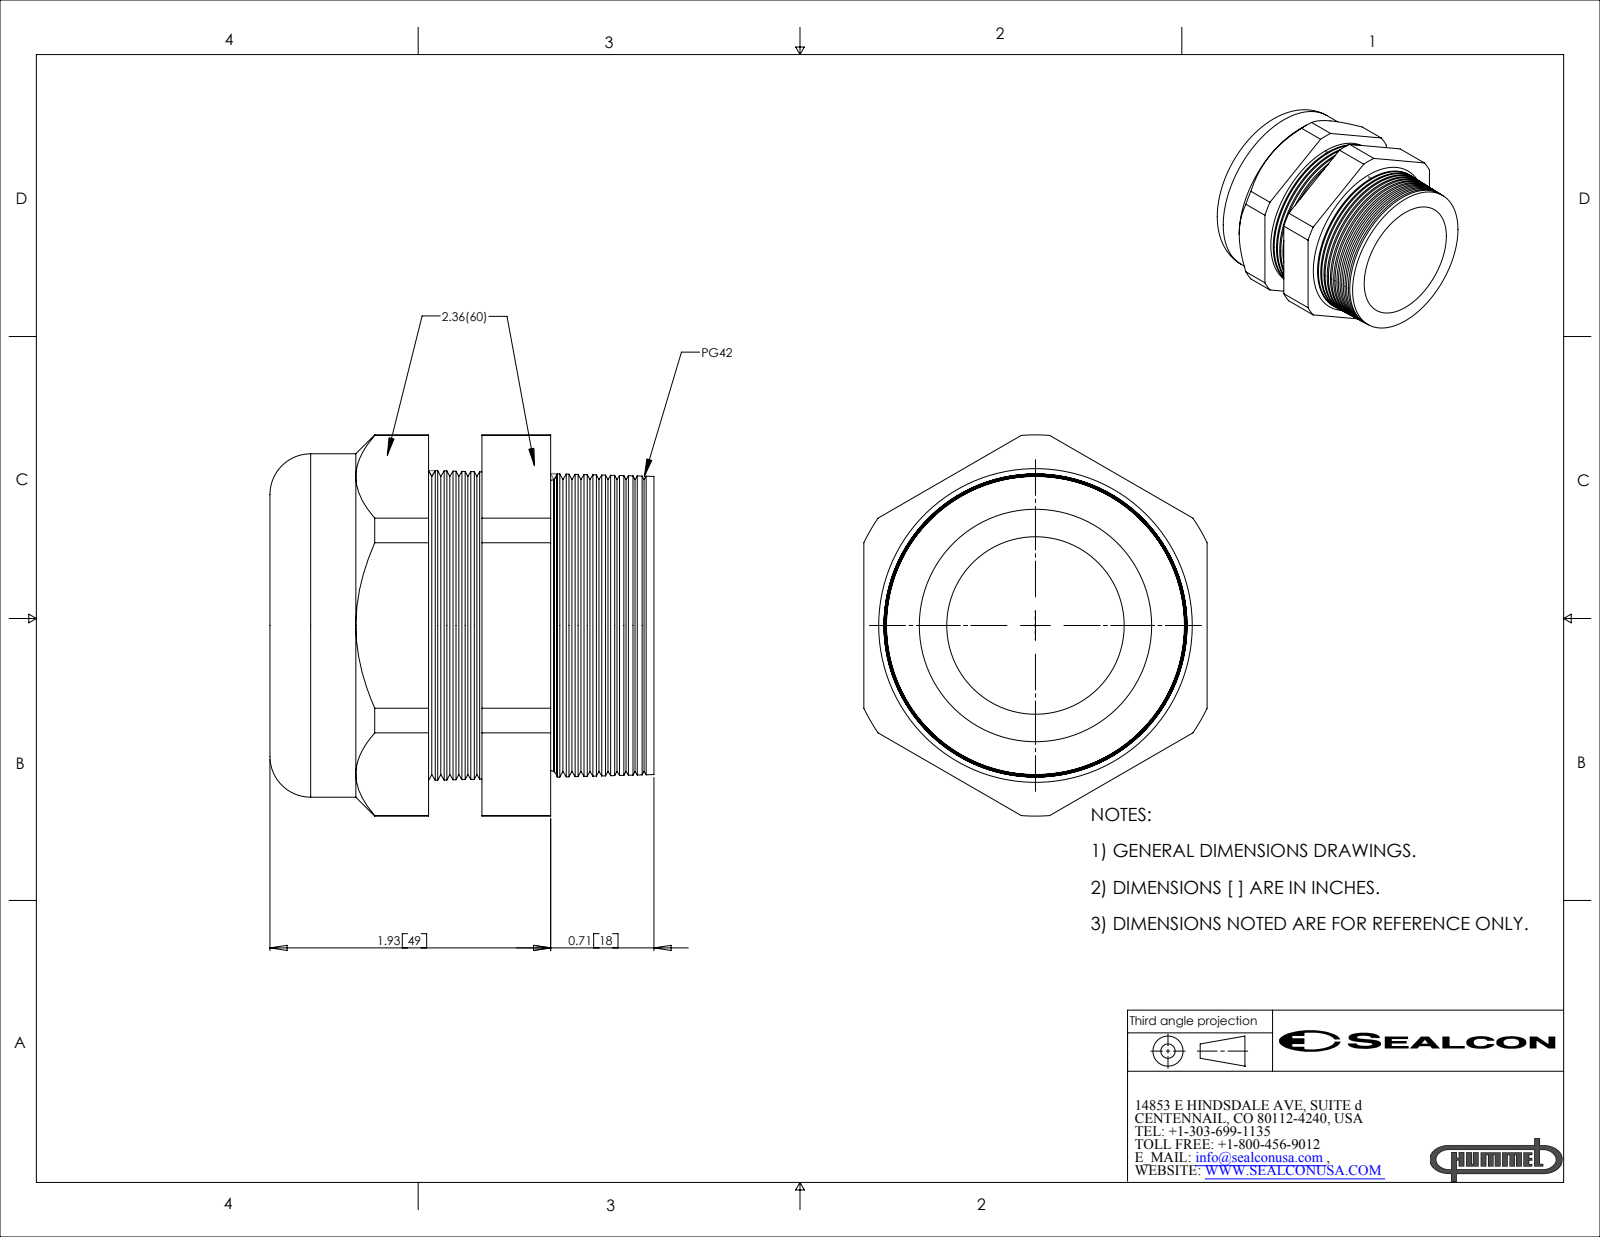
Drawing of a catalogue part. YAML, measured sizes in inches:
part_name: "CD42CR-GY"
step_written_by: "SolidWorks 2007 (CONFIG_CONTROL_DESIGN)"
units: inches
bodies: {solids: 2, faces: 164, planar: 20, cylindrical: 22, other: 122}
overall_size: [2.64, 2.62, 2.36]
volume: 6.964
surface_area: 49.81
round_holes:
  - {diameter: 1.22, count: 1}
  - {diameter: 1.597, count: 1}
round_bosses_or_shafts:
  - {diameter: 2.36, count: 1}
partial_cylinders:
  - {radius: 1.31, count: 1}
face_to_face_distances: [2.36, 0.867, 2.05, 1.182, 0.5, 0.367, 1.55, 1.34, 0.84, 0.472]
